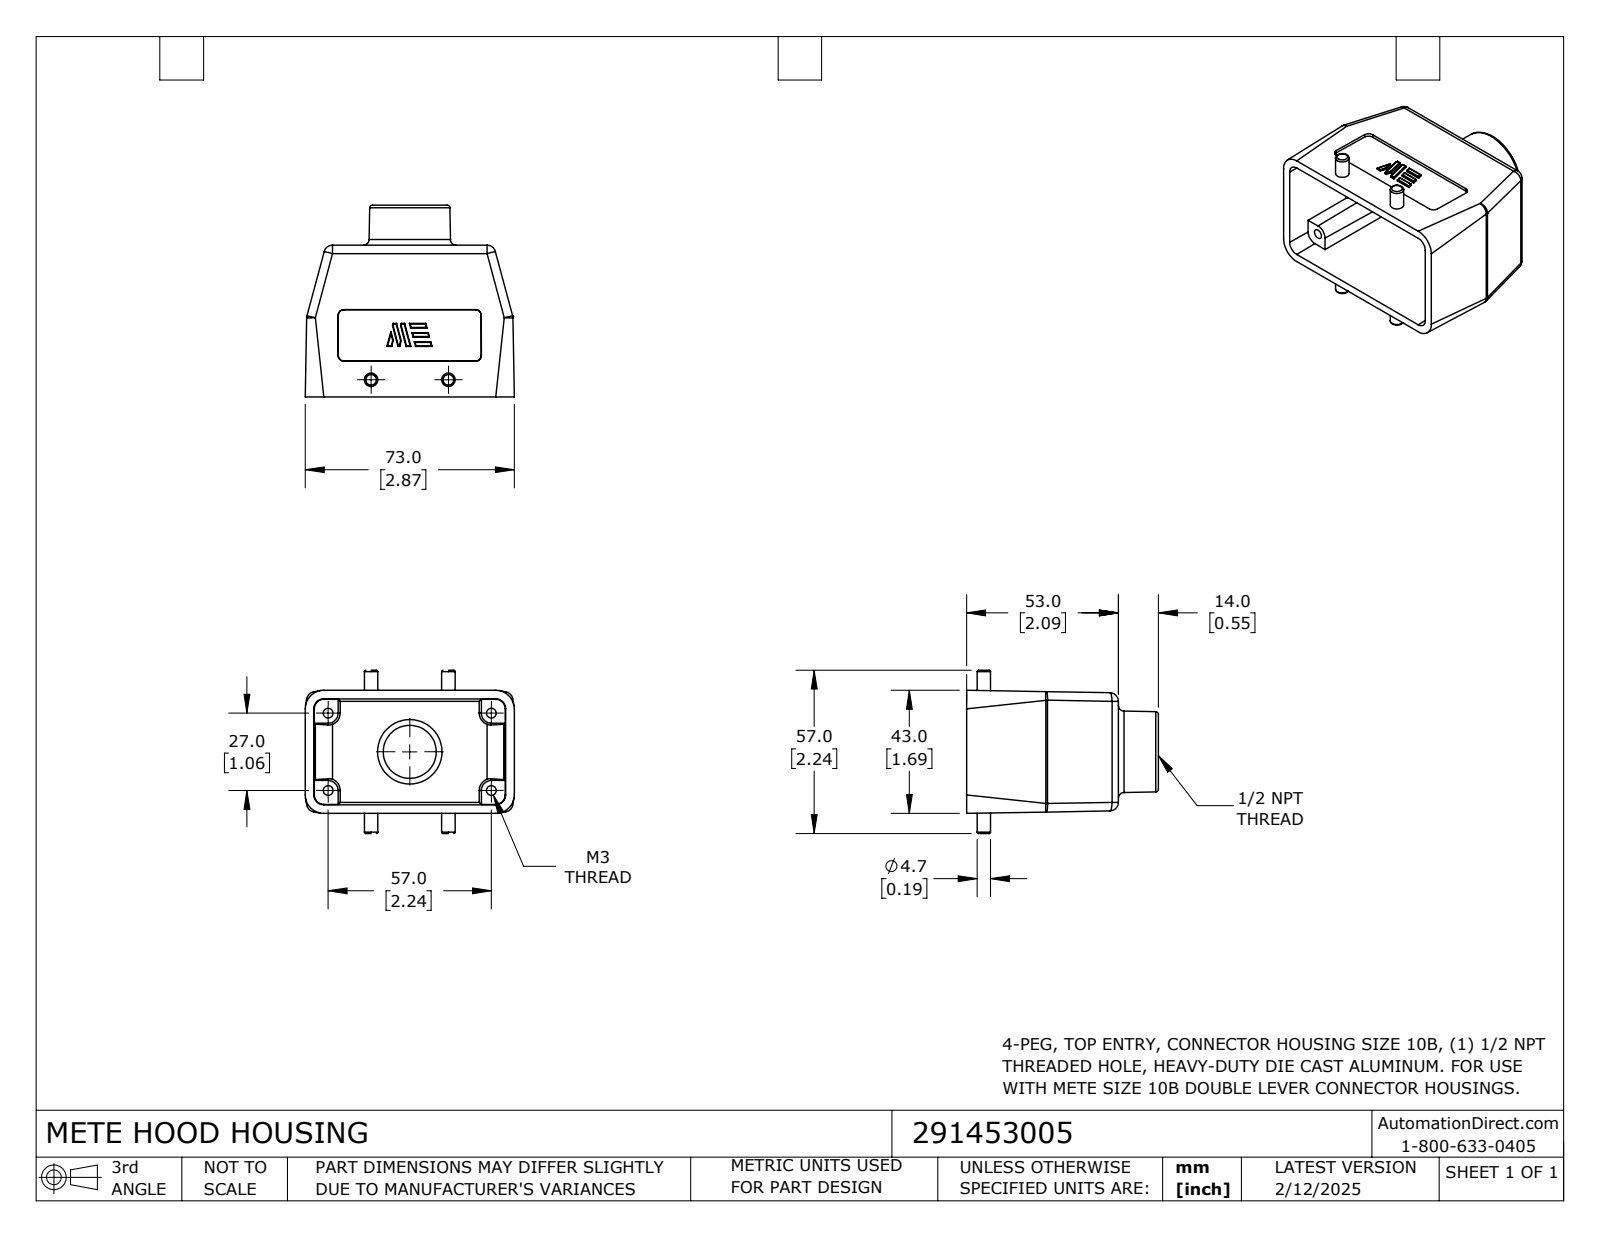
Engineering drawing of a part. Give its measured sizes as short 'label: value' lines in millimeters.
name: 291453005
written by: SolidWorks 2024 (CONFIG_CONTROL_DESIGN)
unit: mm
bodies: 1 solid, 247 faces (113 planar, 92 cylindrical, 42 other)
size: 73 × 67 × 57
volume: 48 830 mm³; area: 28 650 mm²
holes: 4× ⌀3.4, 1× ⌀18.5
bosses: 2× ⌀4.7
rounds: 35× R0.2, 8× R2, 8× R3, 2× R1, 2× R2.5
face distances: 3, 1, 2, 11.4, 8.4, 50, 53, 10.3, 9, 41
hole spacings: 31.5, 27, 57, 63.1
